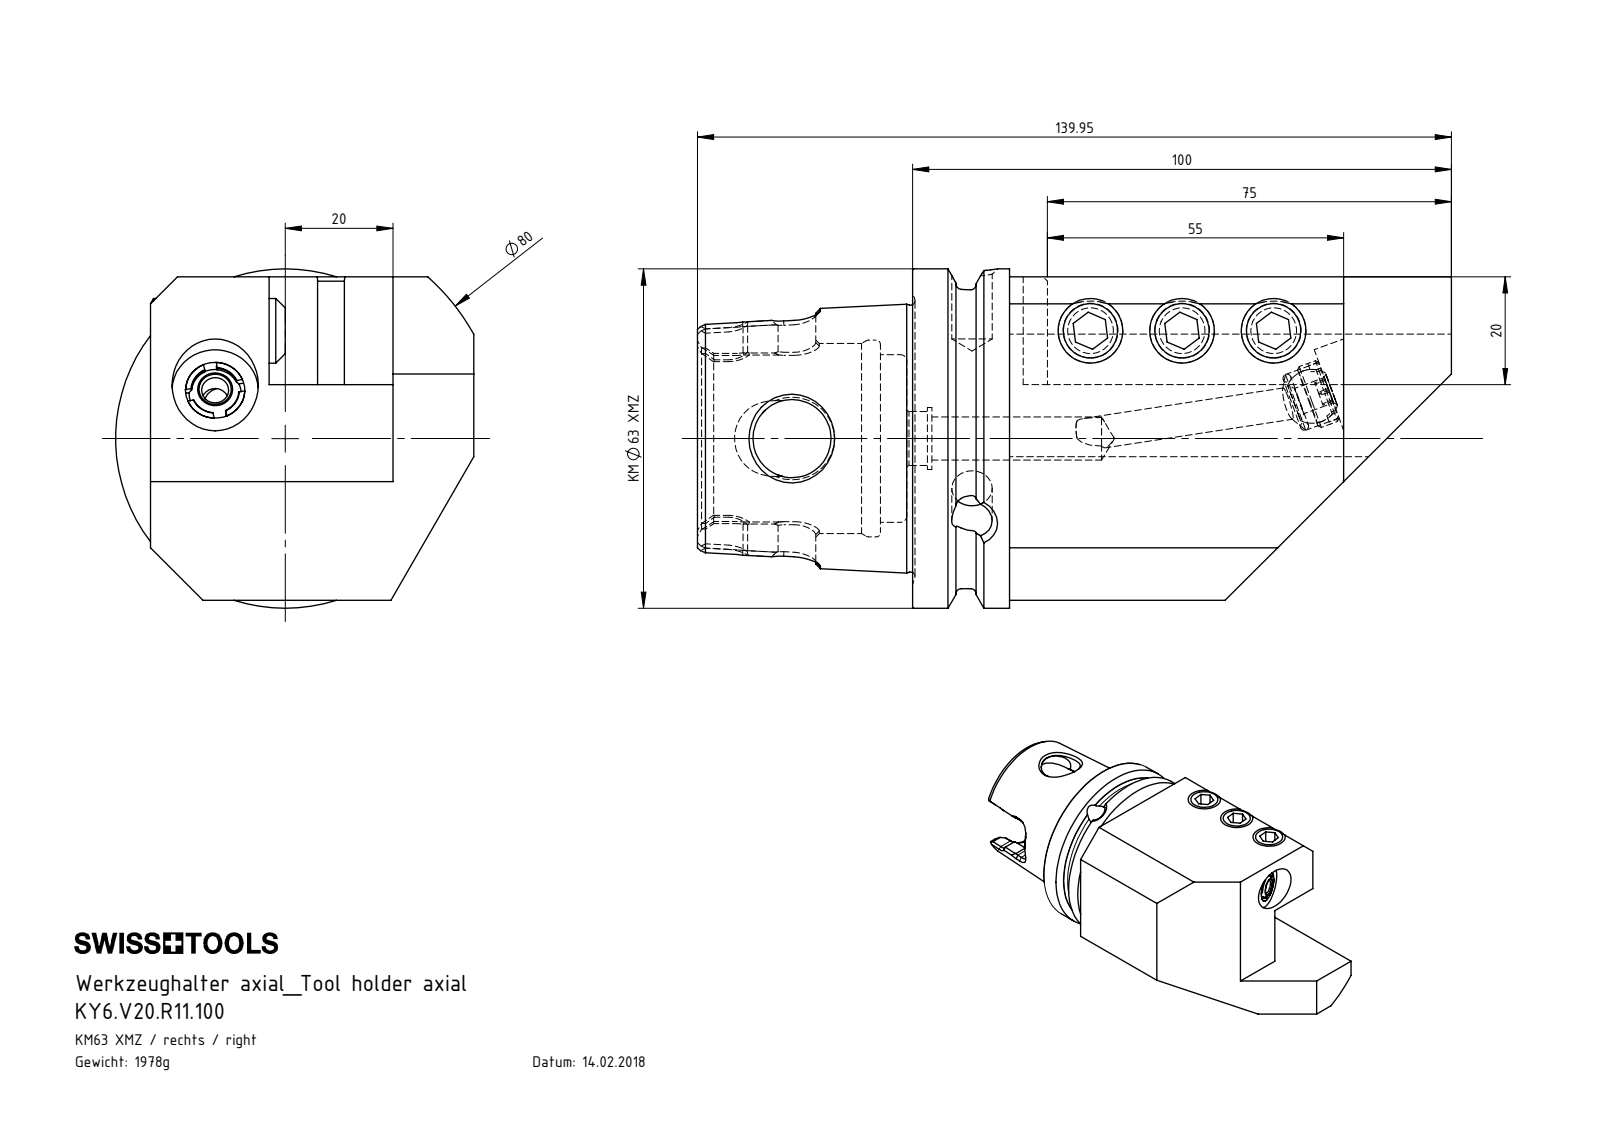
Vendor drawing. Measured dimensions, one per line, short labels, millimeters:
name: KU1-U12.003.010_A; DIN 3771 - 8x1.5; KY6-V20.R11.100_B; ISO 4026 - M12 x 25 (+3 more)
written by: SolidWorks 2017 (CONFIG_CONTROL_DESIGN)
unit: mm
bodies: 7 solids, 344 faces (110 planar, 79 cylindrical, 155 other)
size: 139.95 × 66.47 × 62.95
volume: 251 971 mm³; area: 45 020 mm²
holes: 3× ⌀7.5, 3× ⌀10.2, 2× ⌀10, 1× ⌀5, 1× ⌀6, 1× ⌀8, 1× ⌀11, 1× ⌀11.5, 1× ⌀14.5, 1× ⌀16, 1× ⌀31.1, 1× ⌀35.27
bosses: 4× ⌀12, 1× ⌀62.95, 1× ⌀55.7
rounds: 6× R4, 2× R4.5, 2× R7.04, 1× R4.4, 1× R40
face distances: 60, 20, 15, 45, 40, 38, 23, 22, 80, 18
hole spacings: 17, 34, 58.9, 75.11, 91.61
